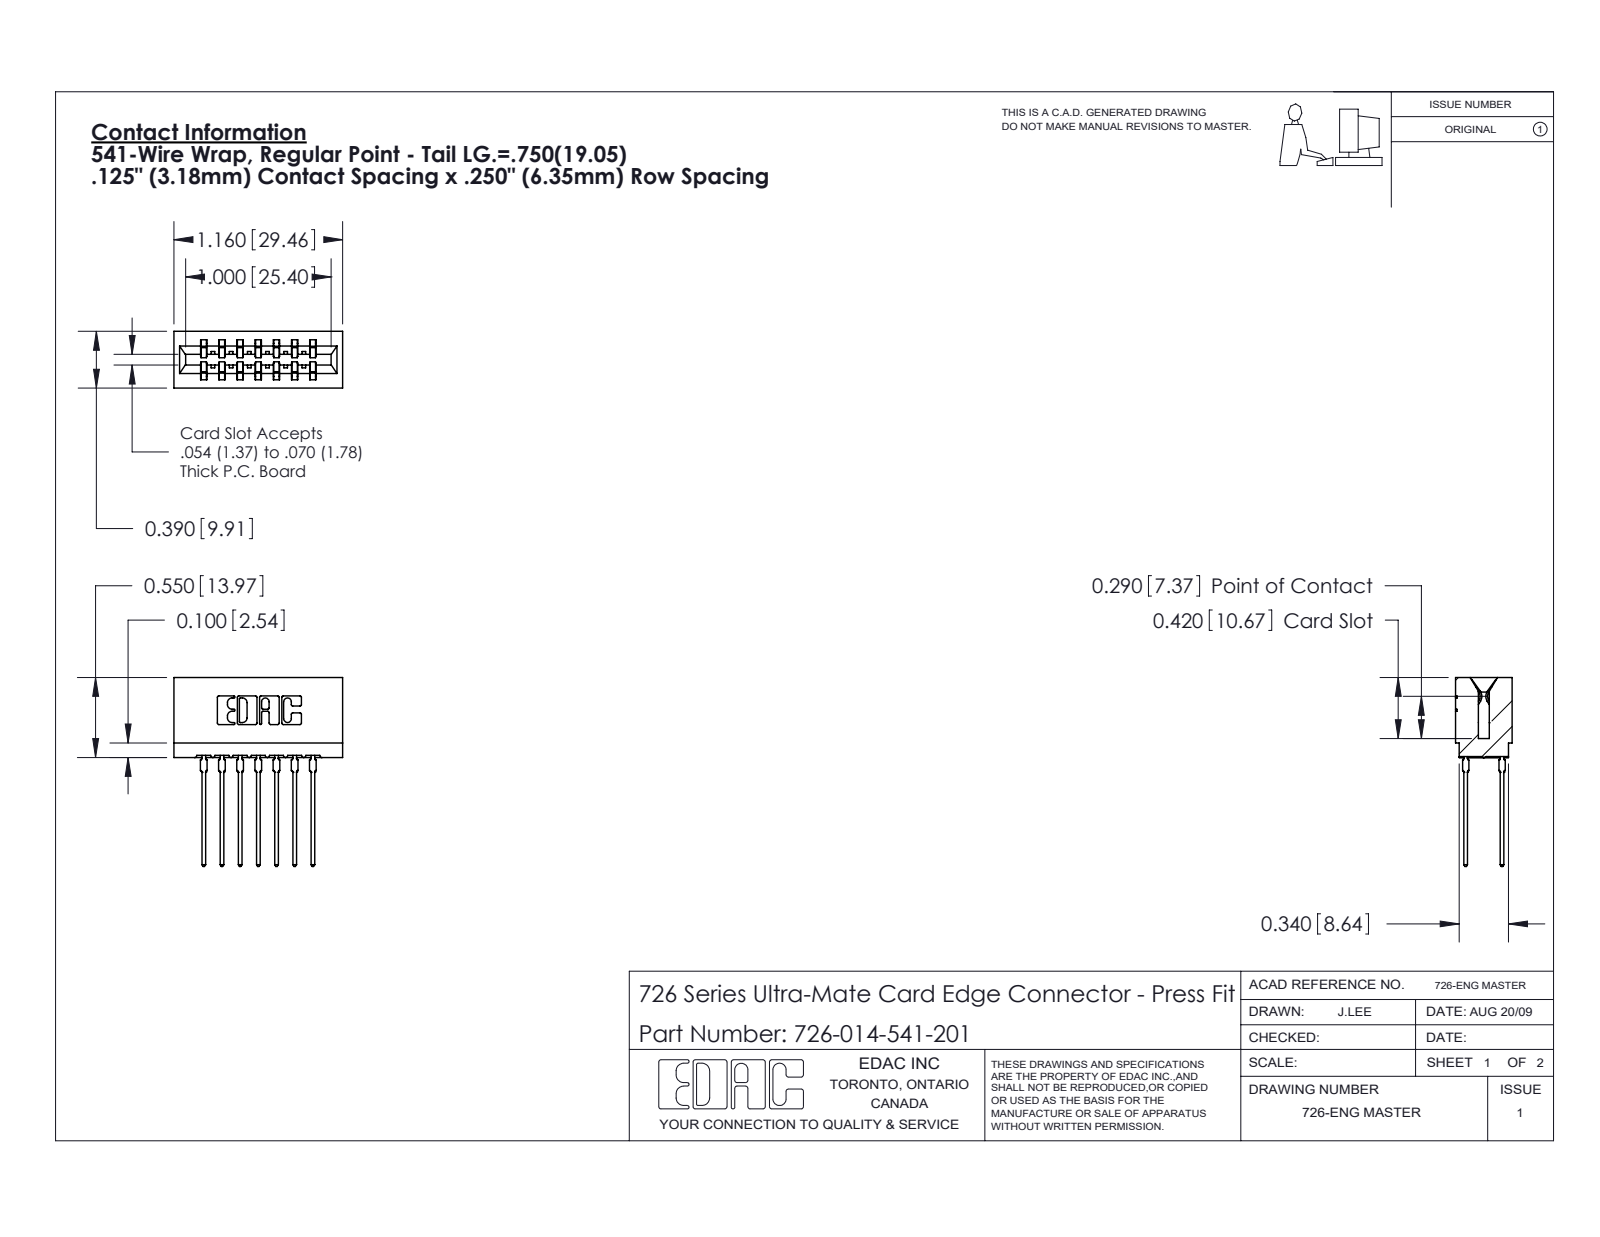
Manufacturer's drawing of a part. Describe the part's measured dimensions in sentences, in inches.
The part is named "726-014-541-201; 746-292-001_541; 726 Part_.515 Slot Depth - 01". Its 3-D file was written by "SolidWorks 2020 (CONFIG_CONTROL_DESIGN)". It is 15 solids with 1350 faces: 699 planar, 287 cylindrical and 364 other. Overall it measures 1.299 by 1.16 by 0.39 inches. Its volume is 0.181 cubic inches and its surface area 7.272 square inches. Partial cylindrical surfaces (rounded edges, fillets, slot ends): 28 of radius 0.021, 22 of radius 0.01, 8 of radius 0.005, 8 of radius 0.011, 8 of radius 0.015, 6 of radius 0.007, 6 of radius 0.031, 3 of radius 0.026. The main face-to-face distances are 0.25, 0.057, 0.333, 0.042, 0.083, 0.125, 0.125, 0.025, 0.5, 0.307.
